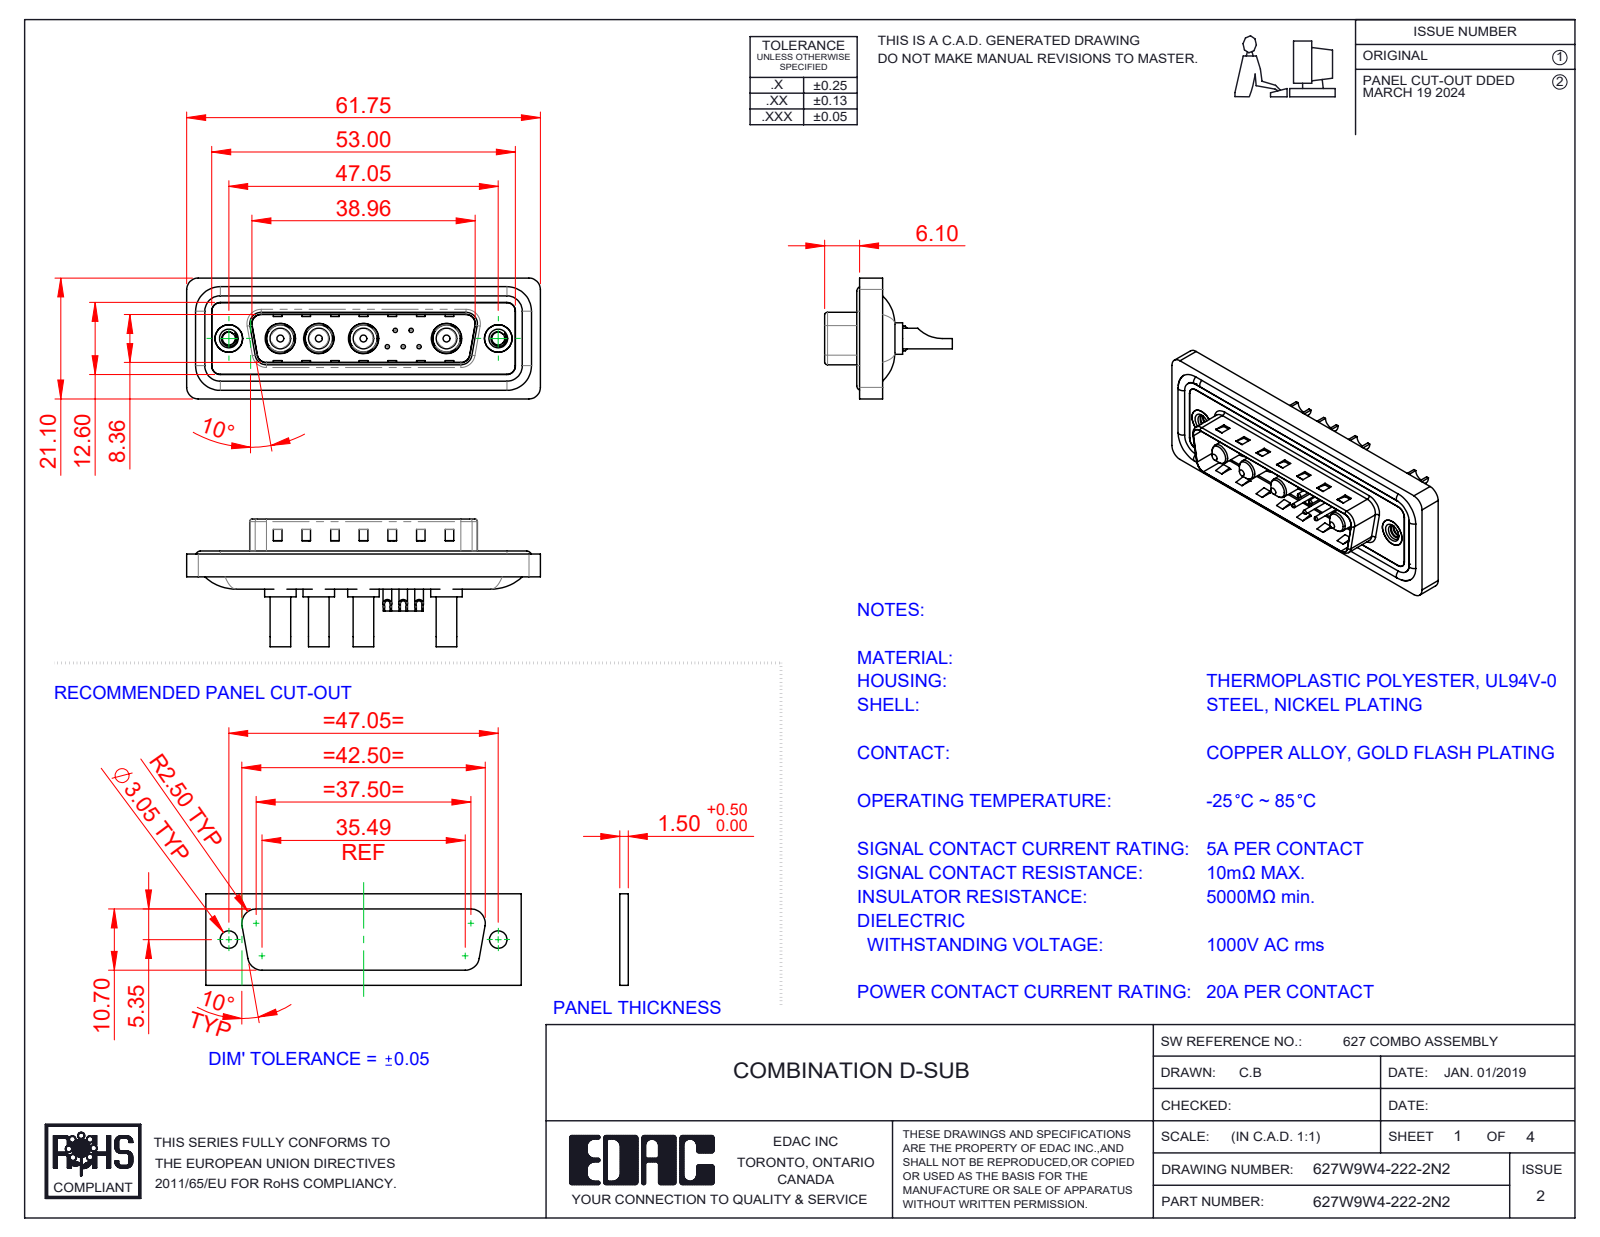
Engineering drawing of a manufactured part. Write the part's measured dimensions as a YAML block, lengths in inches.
part_name: "627Combo Threaded Rivet_2; 627Combo Housing_9W4; 627Combo Contact Row 1_22; 627Combo Contact Row 2_22 (+5 more)"
step_written_by: "SolidWorks 2023 (CONFIG_CONTROL_DESIGN)"
units: inches
bodies: {solids: 20, faces: 852, planar: 306, cylindrical: 356, other: 190}
overall_size: [2.431, 0.878, 0.831]
volume: 0.455
surface_area: 18.92
round_holes:
  - {diameter: 0.03, count: 5}
  - {diameter: 0.039, count: 5}
  - {diameter: 0.063, count: 5}
  - {diameter: 0.079, count: 5}
  - {diameter: 0.106, count: 4}
  - {diameter: 0.191, count: 4}
  - {diameter: 0.209, count: 4}
  - {diameter: 0.089, count: 2}
  - {diameter: 0.157, count: 2}
  - {diameter: 0.189, count: 2}
  - {diameter: 0.197, count: 2}
round_bosses_or_shafts:
  - {diameter: 0.059, count: 5}
  - {diameter: 0.217, count: 4}
  - {diameter: 0.205, count: 4}
  - {diameter: 0.187, count: 4}
  - {diameter: 0.148, count: 4}
  - {diameter: 0.142, count: 4}
  - {diameter: 0.063, count: 4}
  - {diameter: 0.193, count: 2}
partial_cylinders:
  - {radius: 0.059, count: 22}
  - {radius: 0.079, count: 18}
  - {radius: 0.02, count: 8}
  - {radius: 0.063, count: 8}
  - {radius: 0.039, count: 6}
  - {radius: 0.01, count: 4}
  - {radius: 0.024, count: 4}
  - {radius: 0.026, count: 4}
face_to_face_distances: [0.016, 0.059, 0.043, 0.02, 0.063, 0.122, 0.114, 0.032, 0.377, 0.222]
hole_center_spacings: [0.124, 0.109, 0.198, 0.571, 0.109, 0.173, 0.174, 0.197]
